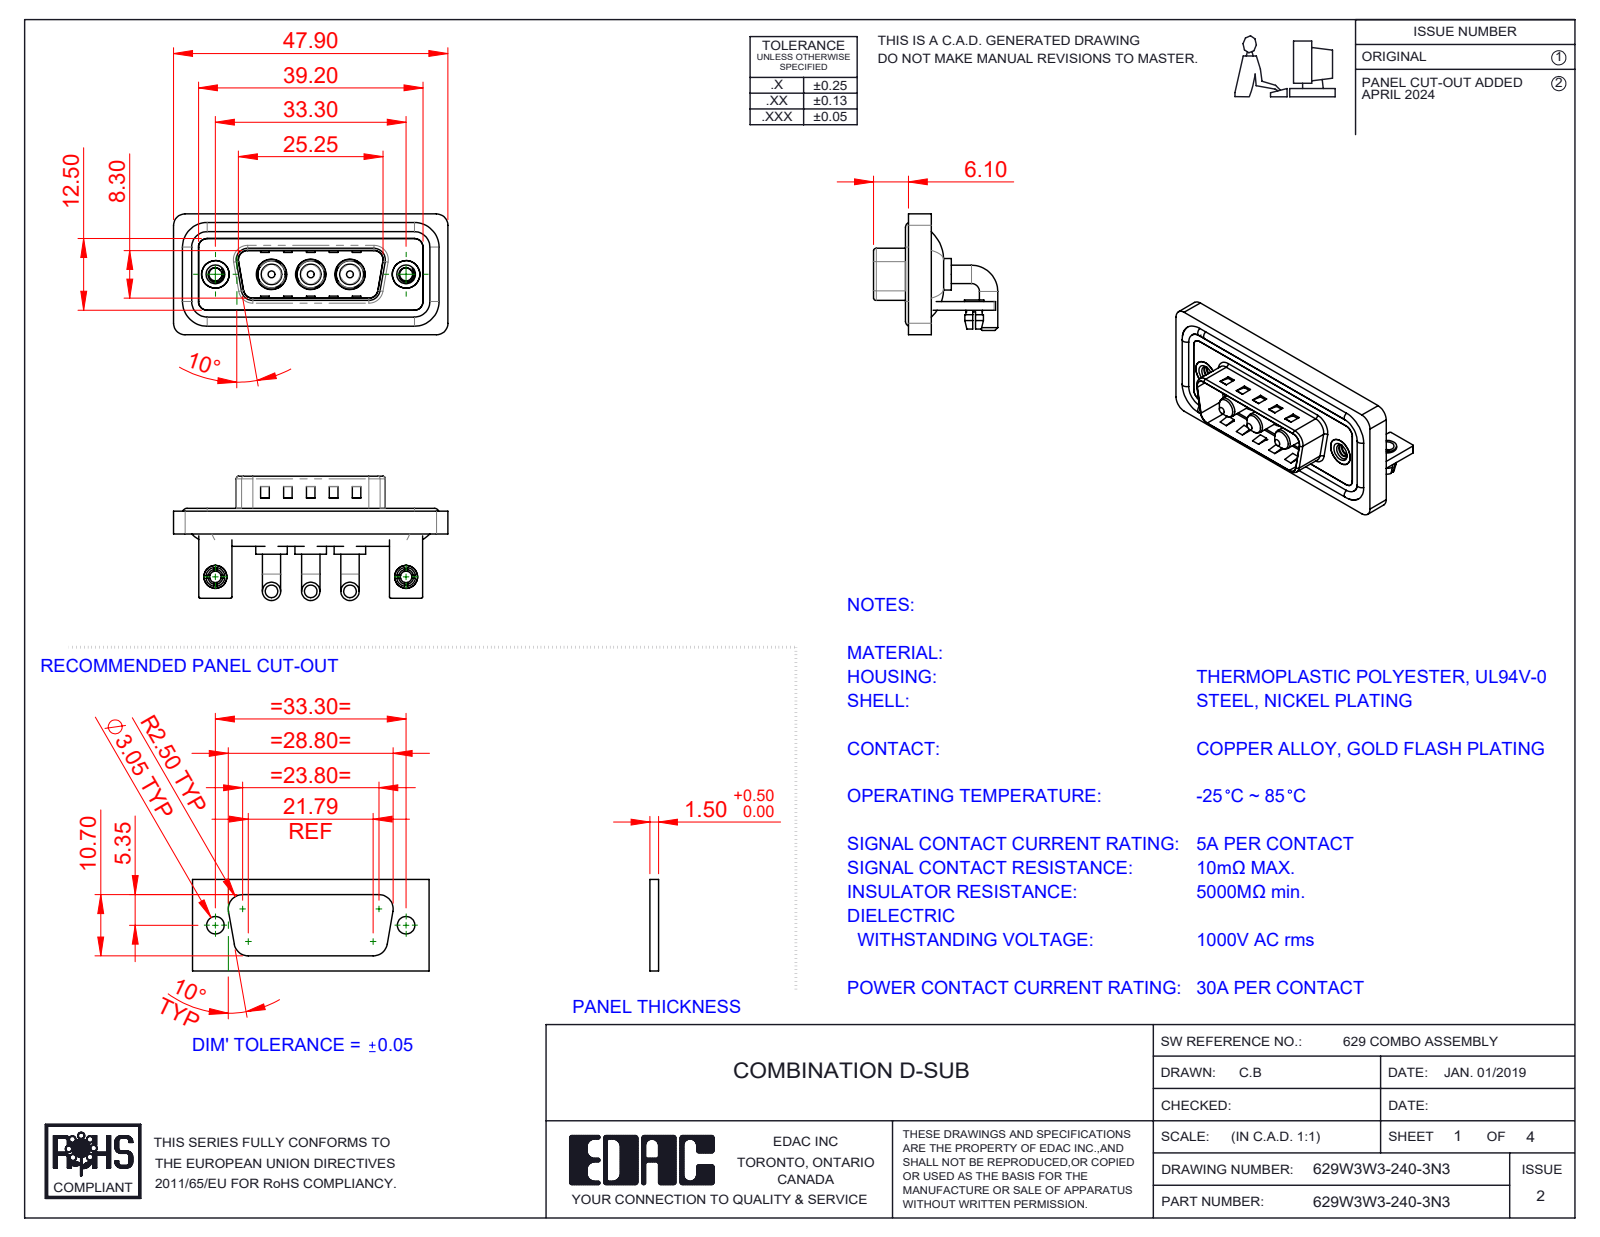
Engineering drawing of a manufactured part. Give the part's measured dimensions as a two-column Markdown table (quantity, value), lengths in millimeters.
| quantity | value |
| --- | --- |
| part name | 629Combo Shell Rear_15 Contacts; 629Combo Board Lock; 629Combo Threaded Rivet_3; 629Combo Stabilizer Bracket (+5 more) |
| STEP written by | SolidWorks 2023 (CONFIG_CONTROL_DESIGN) |
| units | millimeters |
| bodies | 17 solids, 708 faces (275 planar, 297 cylindrical, 136 other) |
| overall size | 47.9 × 21.7 × 21.1 |
| volume | 6 176 mm³ |
| surface area | 9 889 mm² |
| round holes (diameter × count) | 4.85 × 3, 5.3 × 3, 2 × 2, 2.26 × 2, 2.5 × 2, 3.2 × 2, 4 × 2, 4.8 × 2, 5 × 2 |
| round bosses / shafts (diameter × count) | 3.2 × 6, 1.6 × 4, 5.5 × 3, 5.2 × 3, 4.75 × 3, 3.75 × 3, 3.6 × 3, 4.9 × 2 |
| partial cylindrical surfaces (radius × count) | 2 × 21, 1.5 × 18, 0.25 × 16, 0.5 × 9, 1.6 × 8, 0.6 × 4, 0.65 × 4, 0.9 × 4 |
| main face-to-face distances | 0.4, 1.5, 0.8, 2.9, 1.1, 2.1, 3.7, 1.6, 1.2, 4.5 |
| hole center spacings | 6.85, 9.8, 16.65, 23.5, 33.3, 13.7 |
